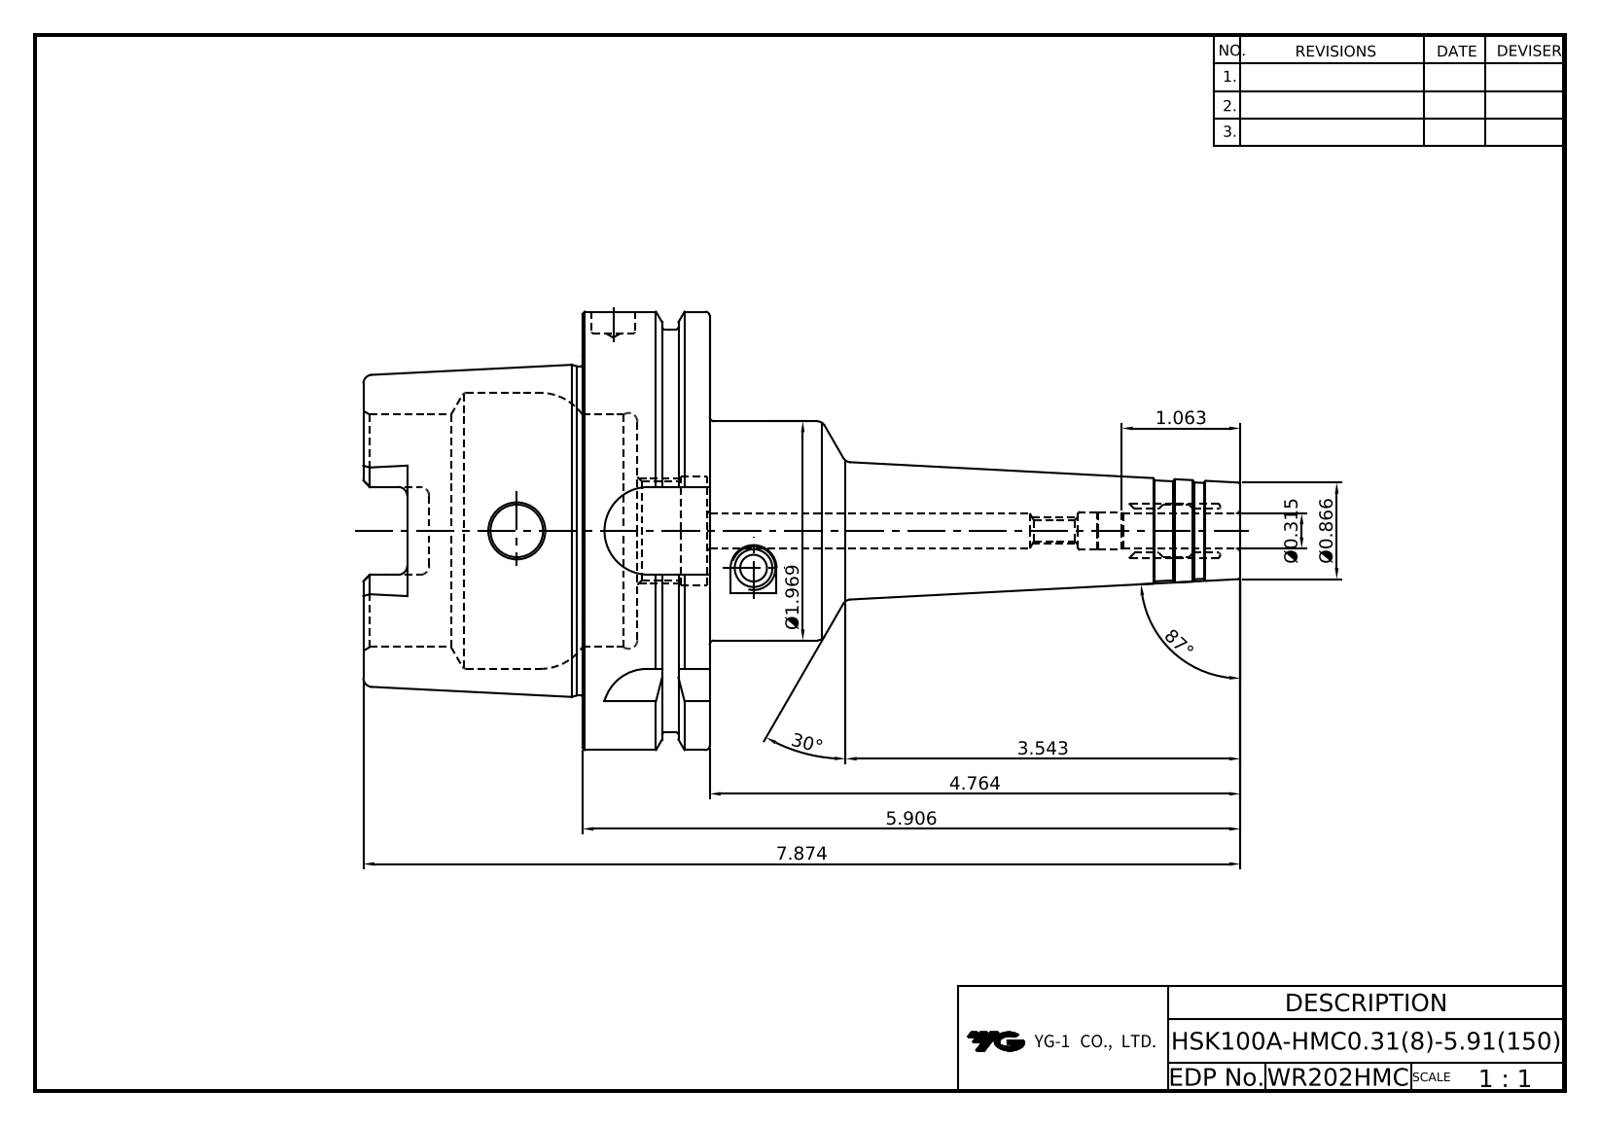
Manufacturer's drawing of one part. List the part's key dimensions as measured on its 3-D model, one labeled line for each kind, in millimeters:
Part name (STEP PRODUCT): LO-HSK100A-HMC8-150
STEP written by: Autodesk Inventor 2020 (AUTOMOTIVE_DESIGN)
Units: millimetres
Bodies: 1 solid, 134 faces (38 planar, 35 cylindrical, 61 other)
Overall size (bounding box): 200 × 100 × 100
Volume: 345 310 mm³ · Surface area: 63 323 mm²
Round holes (diameter × count): ⌀4.92 ×1, ⌀8 ×1, ⌀8.6 ×1, ⌀10 ×1, ⌀12 ×1, ⌀22.38 ×1, ⌀25 ×1, ⌀53 ×1, ⌀63 ×1
Round bosses / shafts (diameter × count): ⌀100 ×1, ⌀92 ×1, ⌀75.41 ×1, ⌀50 ×1
Partial cylindrical surfaces — rounded edges, fillets, slot ends (radius × count): R2 ×6, R4.88 ×4, R10 ×4
Main face-to-face distances: 29, 12.5, 16.5, 62.5, 50, 79, 88, 78.5, 28.5, 16
